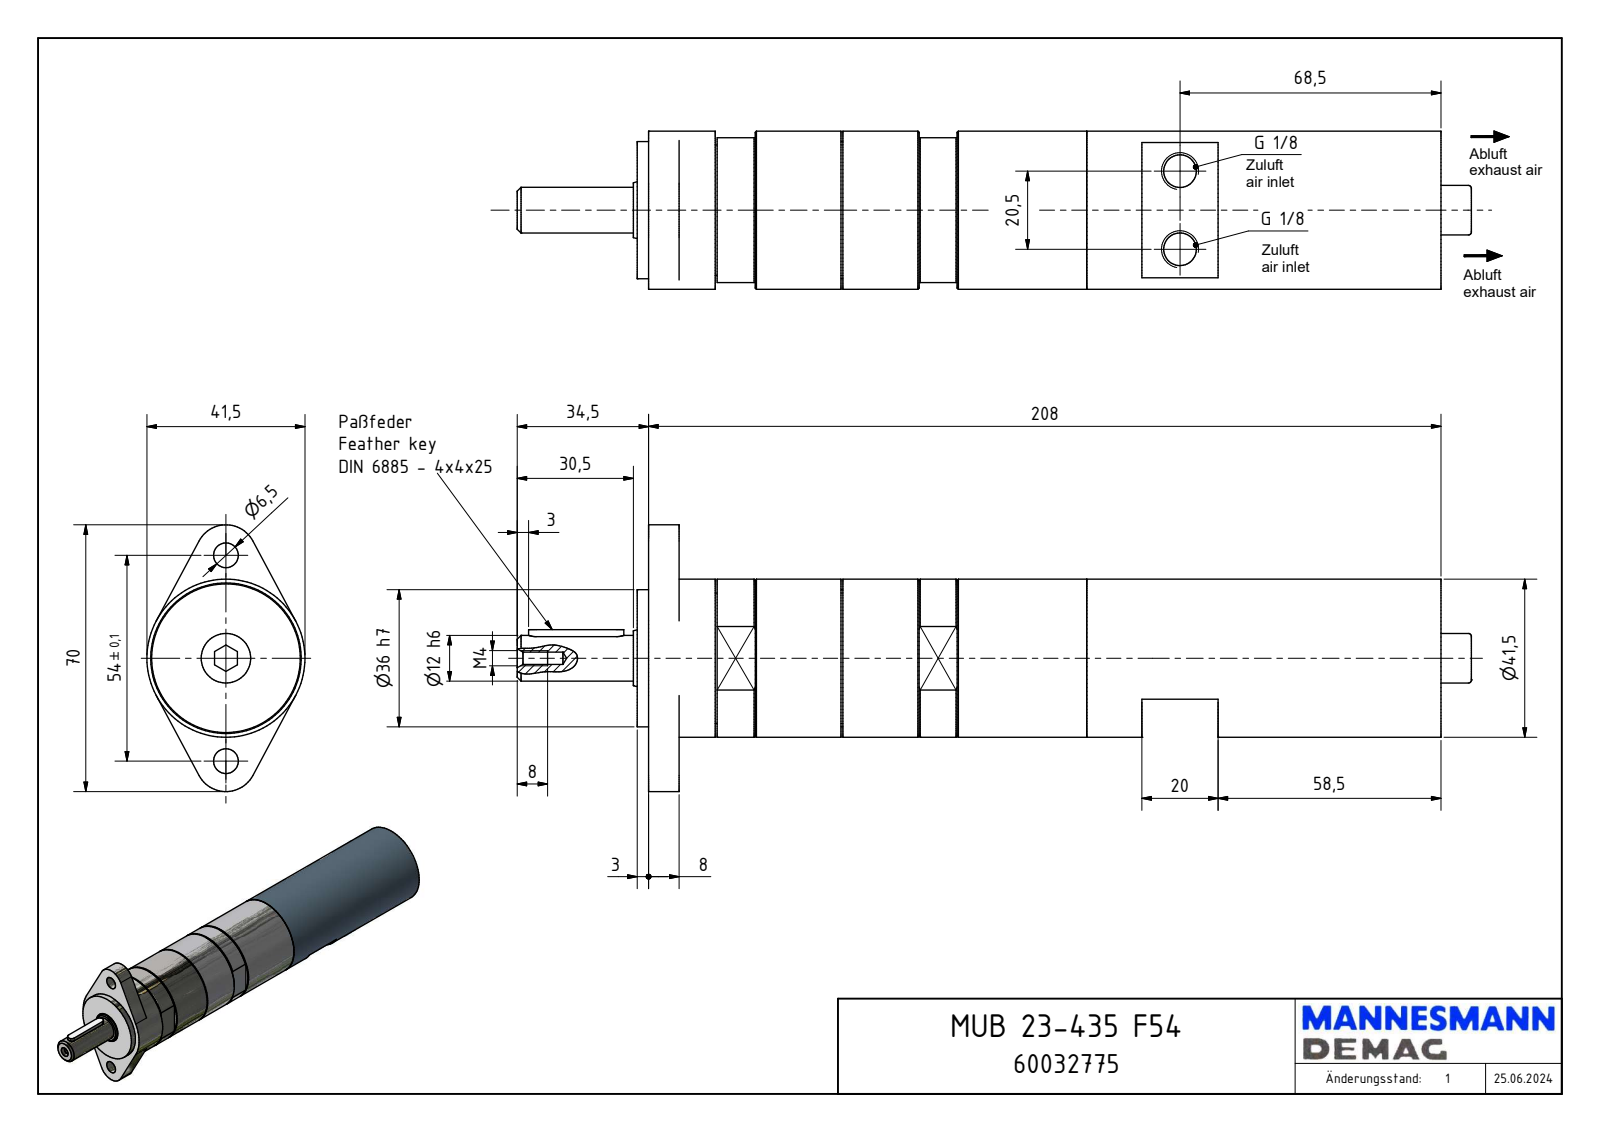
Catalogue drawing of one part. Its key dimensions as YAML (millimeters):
part_name: "MUB 23-435 F54_60032775"
step_written_by: "Autodesk Inventor 2018 (AUTOMOTIVE_DESIGN)"
units: millimeters
bodies: {solids: 1, faces: 139, planar: 69, cylindrical: 51, other: 19}
overall_size: [250.2, 70, 41.5]
volume: 284310
surface_area: 40715
round_holes:
  - {diameter: 2, count: 2}
  - {diameter: 6.5, count: 2}
  - {diameter: 8.57, count: 2}
  - {diameter: 3.24, count: 1}
  - {diameter: 8.5, count: 1}
  - {diameter: 13, count: 1}
  - {diameter: 16, count: 1}
  - {diameter: 37, count: 1}
  - {diameter: 38.01, count: 1}
  - {diameter: 39.5, count: 1}
round_bosses_or_shafts:
  - {diameter: 41.5, count: 1}
  - {diameter: 39, count: 1}
  - {diameter: 36, count: 1}
  - {diameter: 24.32, count: 1}
  - {diameter: 14.95, count: 1}
  - {diameter: 12, count: 1}
  - {diameter: 8, count: 1}
partial_cylinders:
  - {radius: 2, count: 4}
  - {radius: 1.6, count: 2}
  - {radius: 2.5, count: 2}
  - {radius: 8, count: 2}
  - {radius: 8.1, count: 1}
face_to_face_distances: [207.7, 3, 210.7, 82, 128.62, 125.62, 82.08, 128.7, 125.7, 155.92]
hole_center_spacings: [12.94, 26.75, 27, 32.82, 20.5, 25, 54]
